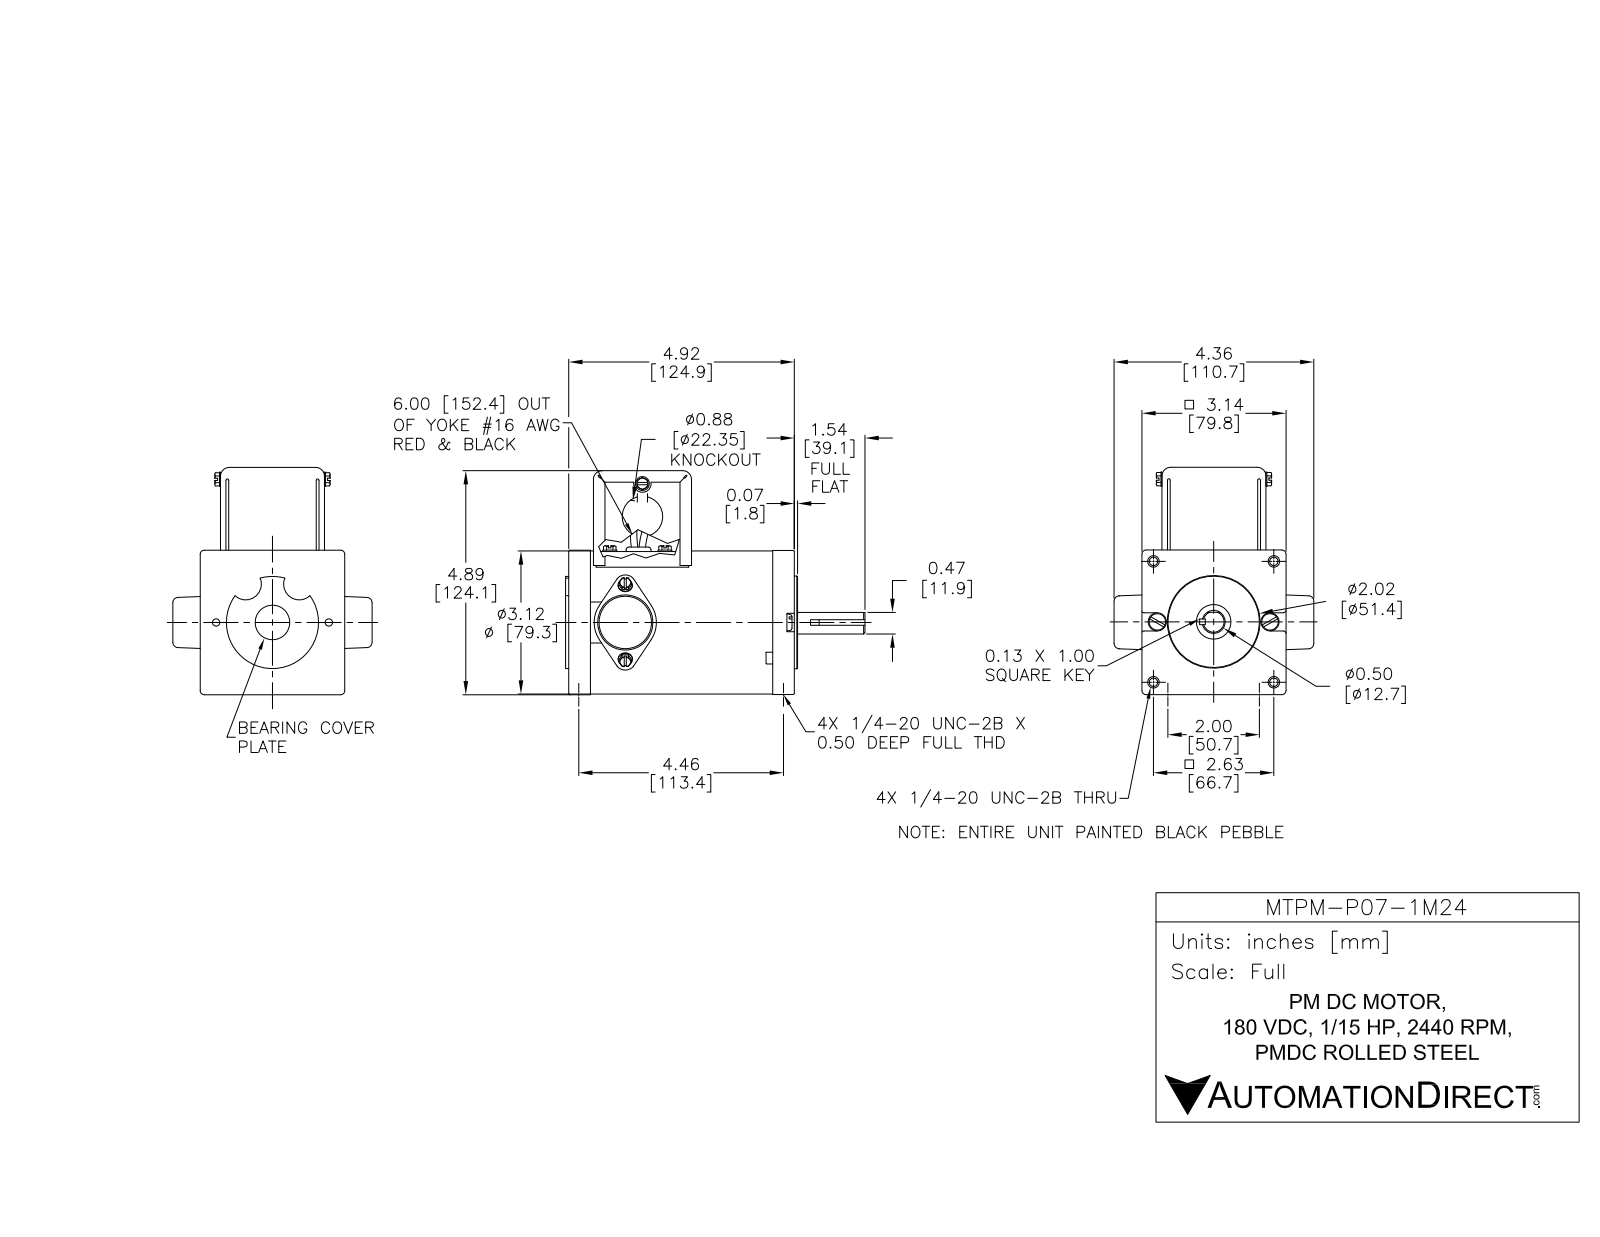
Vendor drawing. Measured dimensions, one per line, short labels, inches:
name: MTPM-P07-1M24
written by: SolidWorks 2017 (AUTOMOTIVE_DESIGN)
unit: in
bodies: 28 solids, 410 faces (271 planar, 114 cylindrical, 25 other)
size: 6.52 × 4.944 × 4.39
volume: 12.13 in³; area: 231.8 in²
holes: 4× ⌀0.125, 2× ⌀0.198, 1× ⌀0.25, 1× ⌀0.3, 1× ⌀0.375, 1× ⌀0.5, 1× ⌀1.225, 1× ⌀2.02, 1× ⌀3, 1× ⌀3.125
bosses: 4× ⌀0.3, 2× ⌀0.125, 2× ⌀0.1, 1× ⌀0.625
rounds: 4× R0.191, 4× R0.234, 2× R0.159, 2× R0.341, 1× R0.151, 1× R0.613, 1× R0.667, 1× R0.678
face distances: 0.031, 0.25, 4.665, 0.063, 2.135, 4.415, 2.047, 0.094, 4.915, 2.198
hole spacings: 1.318, 1.859, 2.63, 2.865, 1.23, 3.719, 2.46, 3.083
